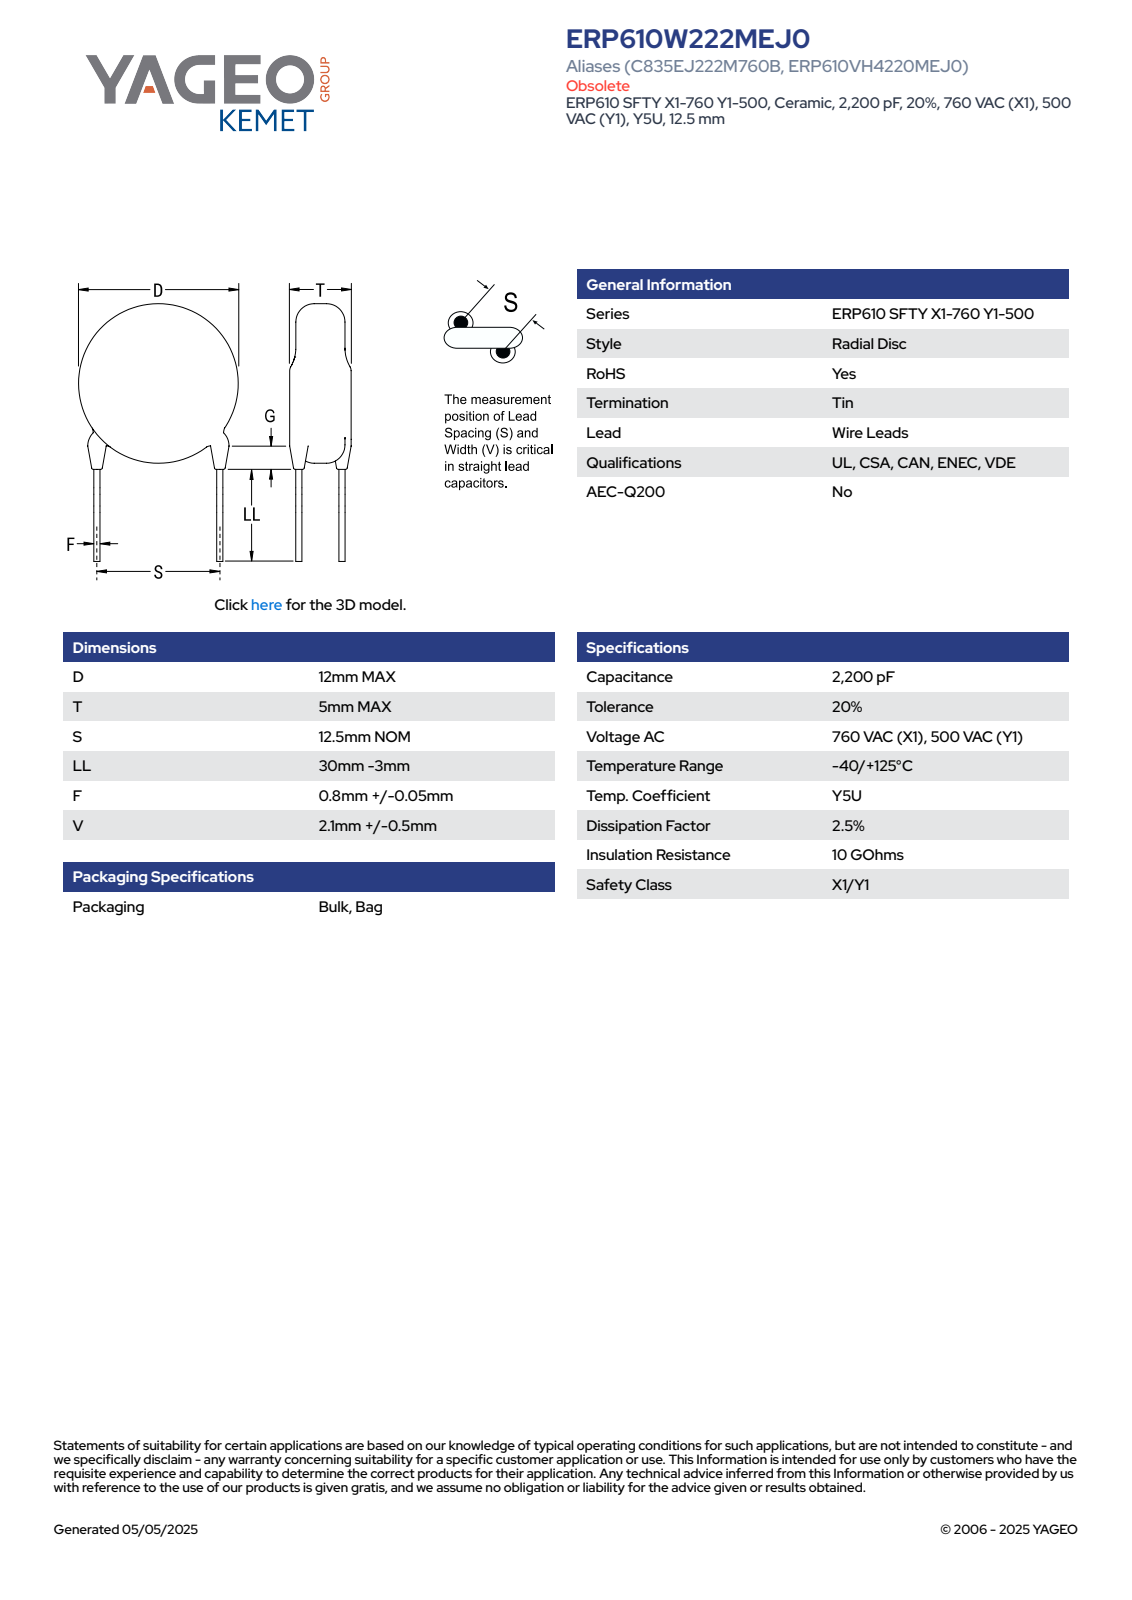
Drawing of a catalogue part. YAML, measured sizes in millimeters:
part_name: "CCD_KST_12X5_D12T5S12.5LL27F0.85G3V2.6"
step_written_by: "SolidWorks 2014 (AUTOMOTIVE_DESIGN)"
units: millimeters
bodies: {solids: 4, faces: 83, planar: 61, cylindrical: 10, other: 12}
overall_size: [39.2, 13.08, 5]
volume: 585
surface_area: 555
round_bosses_or_shafts:
  - {diameter: 0.85, count: 4}
  - {diameter: 12, count: 1}
face_to_face_distances: [5, 33.94, 32.45, 1.49, 0.41, 0.37, 6.1, 3.08, 4.43, 4.6]
